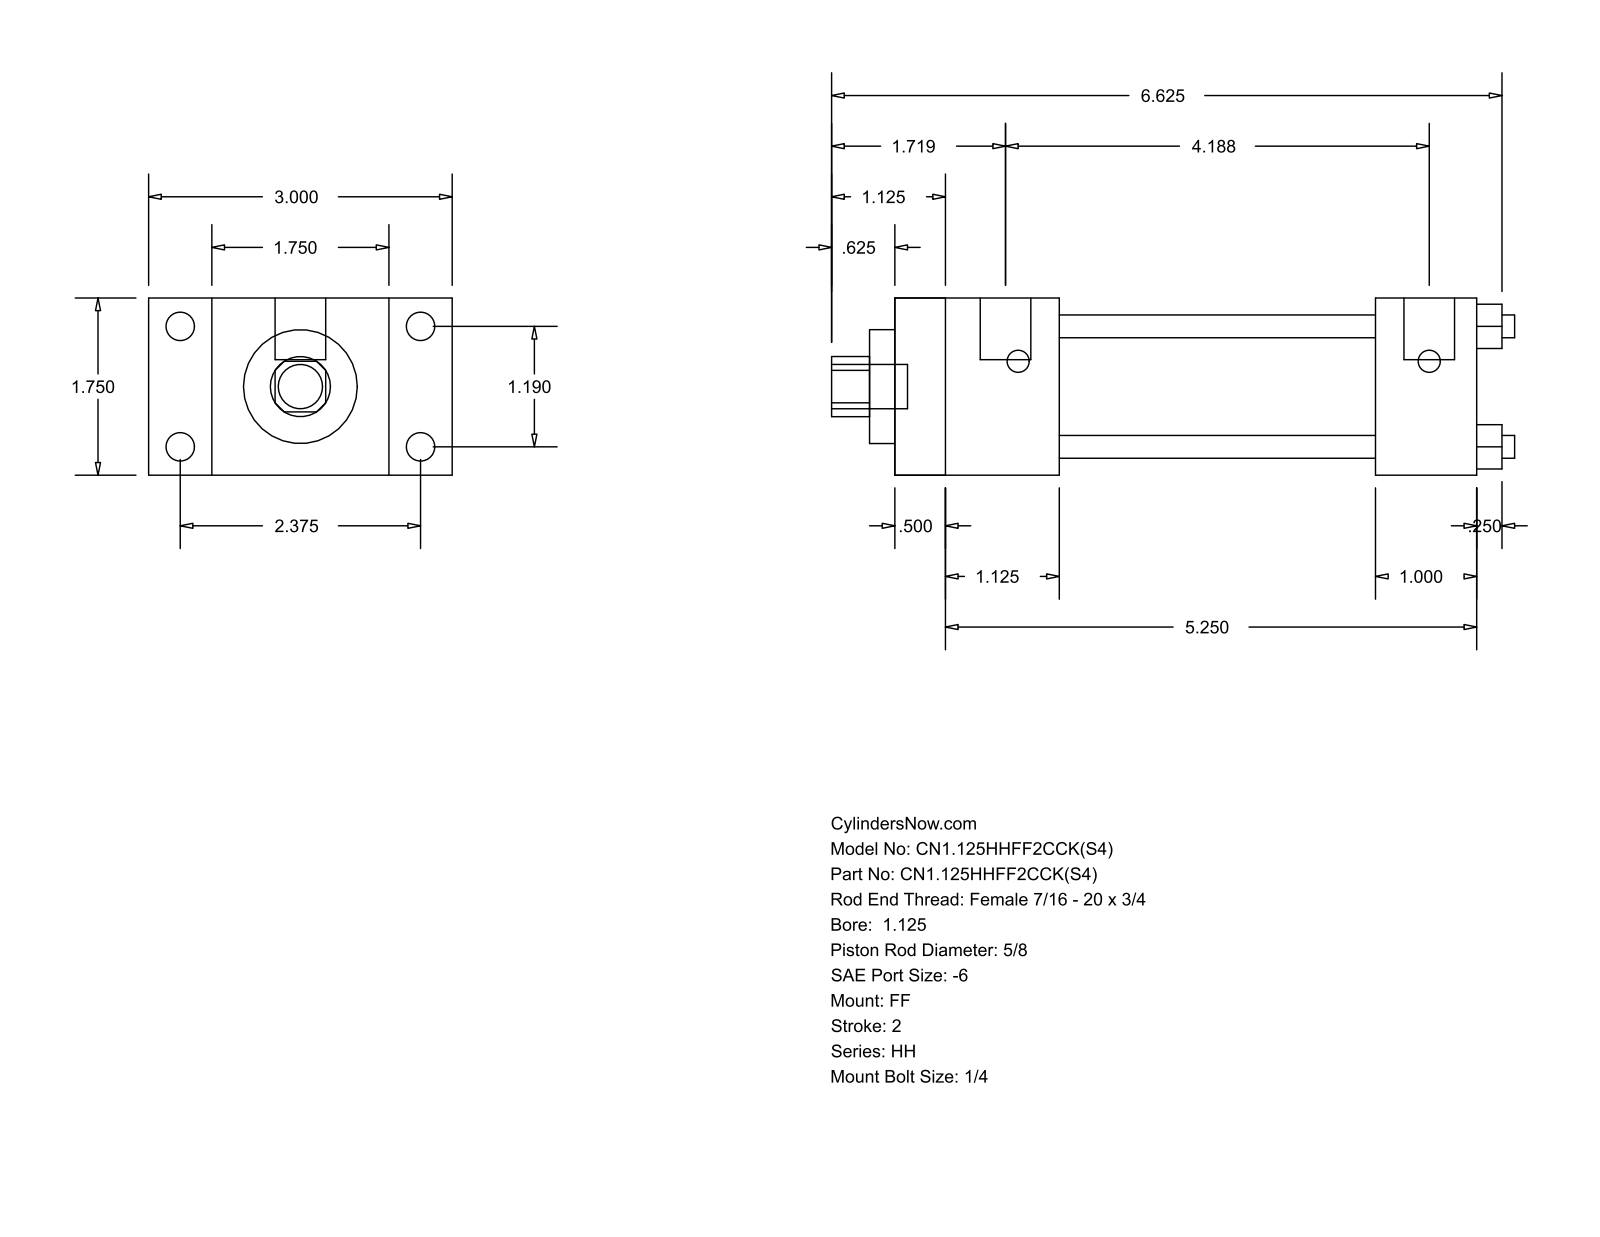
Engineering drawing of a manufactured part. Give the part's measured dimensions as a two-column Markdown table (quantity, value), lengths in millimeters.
| quantity | value |
| --- | --- |
| part name | HH_FF__0112_0.625 |
| STEP written by | GSSL Pune (CONFIG_CONTROL_DESIGN) |
| units | millimeters |
| bodies | 0 solids, 92 faces (64 planar, 28 cylindrical, 0 other) |
| overall size | 171.45 × 76.2 × 44.45 |
| round holes (diameter × count) | 5.71 × 4, 15.88 × 1, 28.57 × 1, 34.92 × 1 |
| round bosses / shafts (diameter × count) | 7.14 × 4, 5.56 × 4, 12.7 × 2, 11.11 × 1 |
| partial cylindrical surfaces (radius × count) | 7.54 × 1 |
| main face-to-face distances | 44.46, 146.05, 12.69, 133.36, 15.87, 60.33, 28.58, 41.27, 120.65, 107.96 |
| hole center spacings | 21.37, 30.22, 42.74 |
